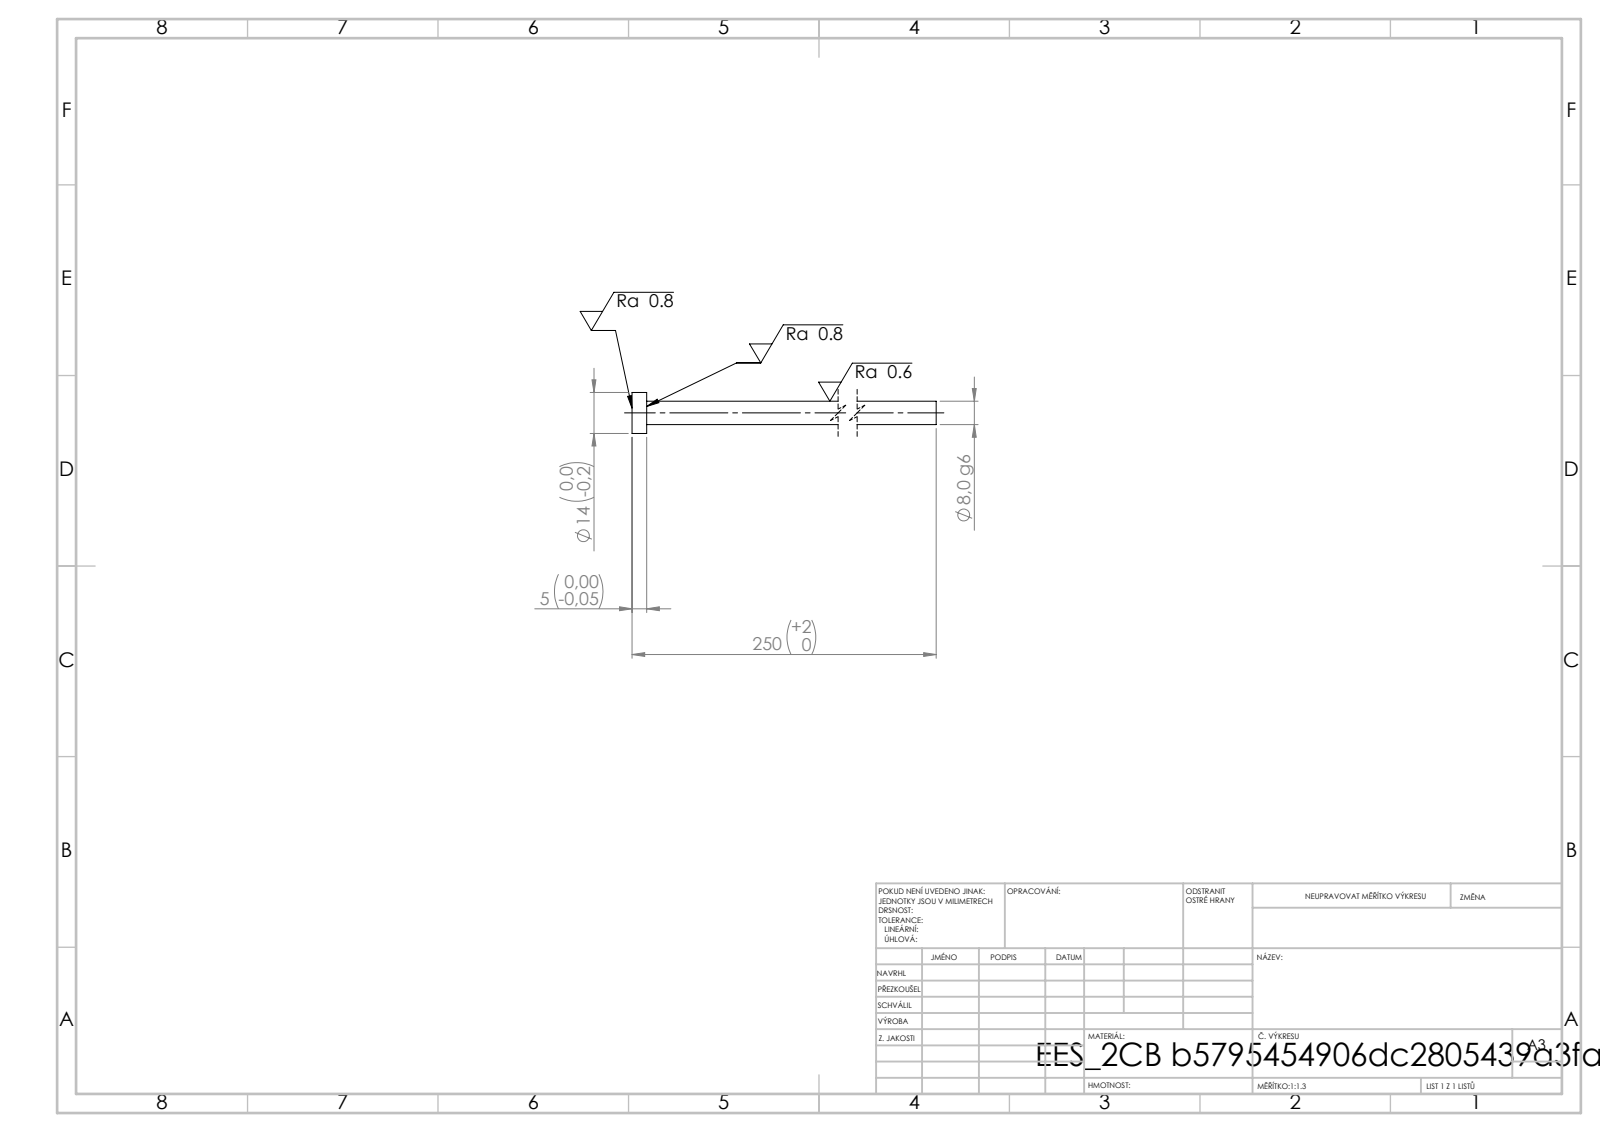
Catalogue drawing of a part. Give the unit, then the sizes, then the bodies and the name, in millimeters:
Units: millimetres
Overall size (bounding box): 250 × 14 × 14
Round bosses / shafts (diameter × count): ⌀14 ×1, ⌀8 ×1
Main face-to-face distances: 5, 250, 245
Volume: 13 085 mm³ · Surface area: 6 685 mm²
Bodies: 1 solid, 7 faces (3 planar, 4 cylindrical, 0 other)
STEP written by: SolidWorks 2019 (CONFIG_CONTROL_DESIGN)
